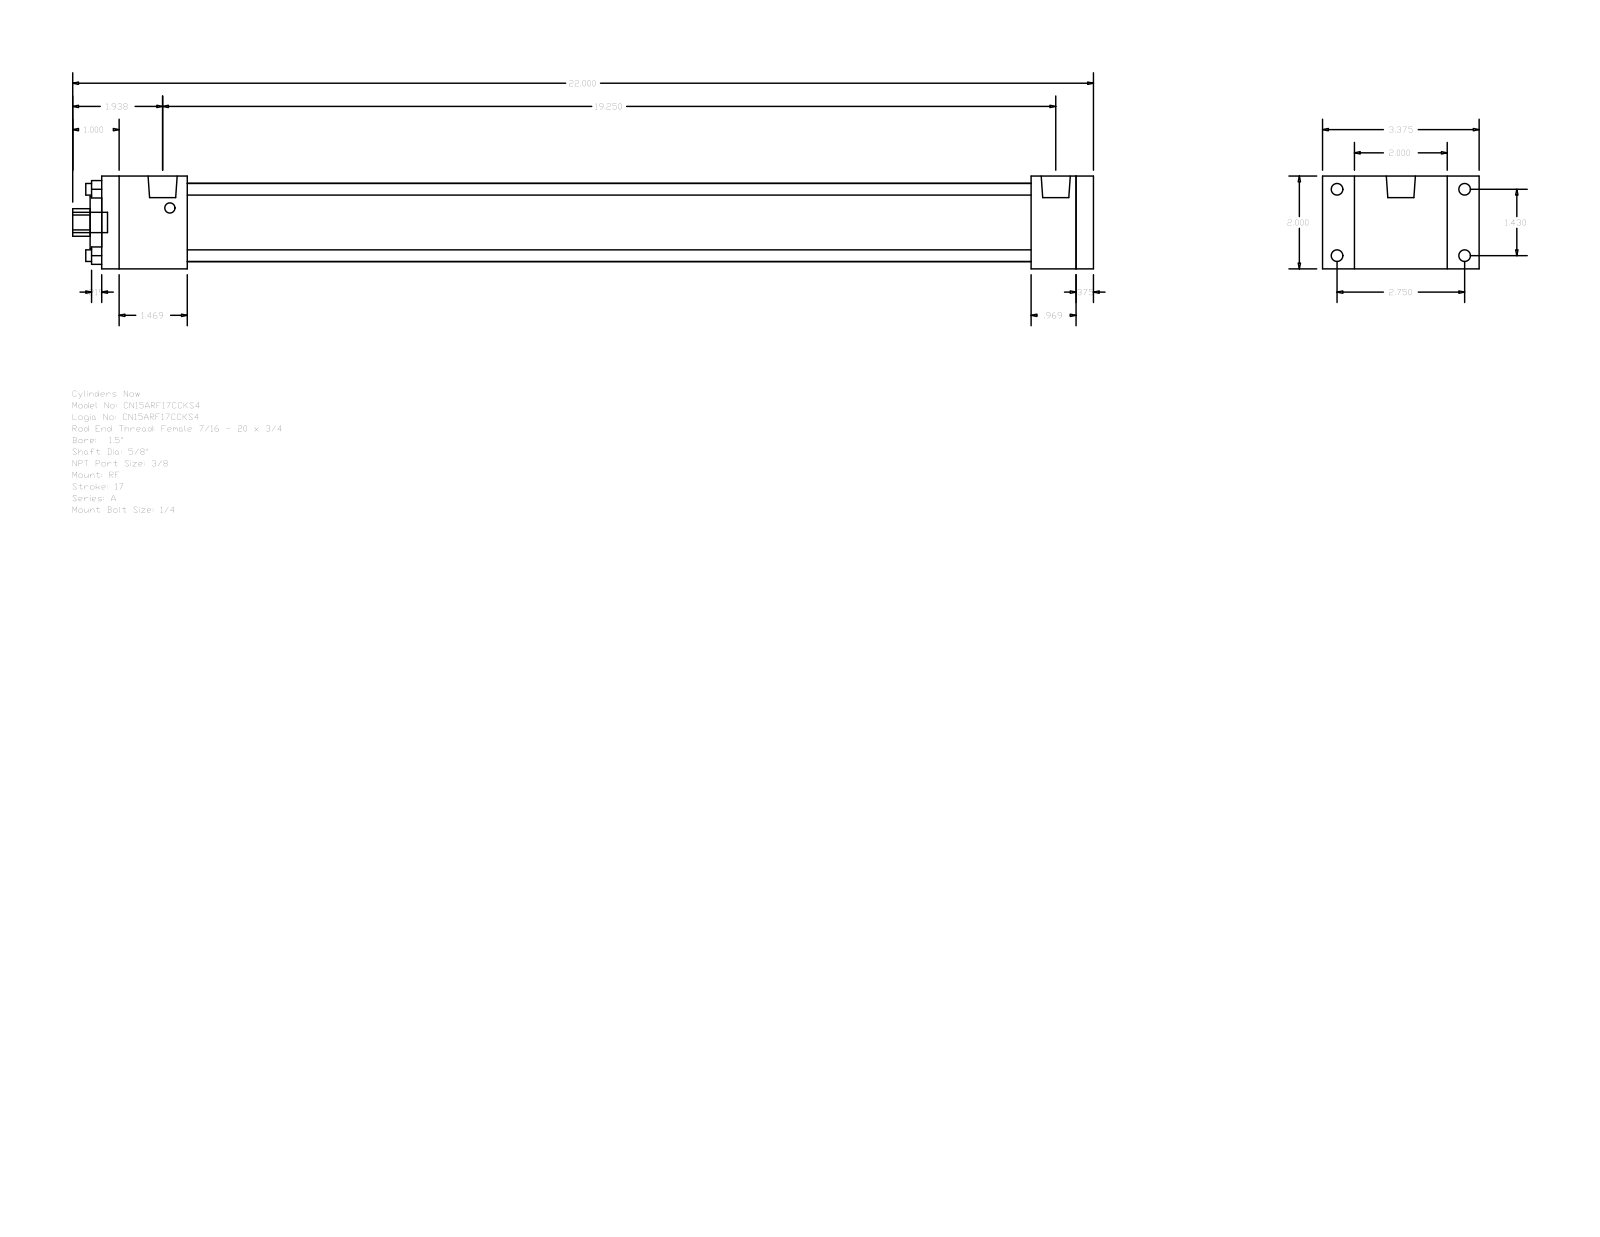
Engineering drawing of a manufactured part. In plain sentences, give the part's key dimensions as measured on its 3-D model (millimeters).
The part is named "A_RF__0150_0.625". Its 3-D file was written by "GSSL Pune (CONFIG_CONTROL_DESIGN)". It is 0 solids with 92 faces: 64 planar, 28 cylindrical and 0 other. Overall it measures 558.8 by 85.72 by 50.8 millimeters. Round holes: 4 of diameter 6.35, 1 of diameter 15.88, 1 of diameter 28.57, 1 of diameter 42.93. Round bosses or shafts: 4 of diameter 6.35, 4 of diameter 5.56, 2 of diameter 15.93, 1 of diameter 11.11. Partial cylindrical surfaces (rounded edges, fillets, slot ends): 1 of radius 7.54. The main face-to-face distances are 50.8, 9.53, 542.92, 533.39, 508.79, 24.6, 34.13, 46.83, 461.96, 486.56. The hole center spacings are 25.68, 36.32, 51.36.
